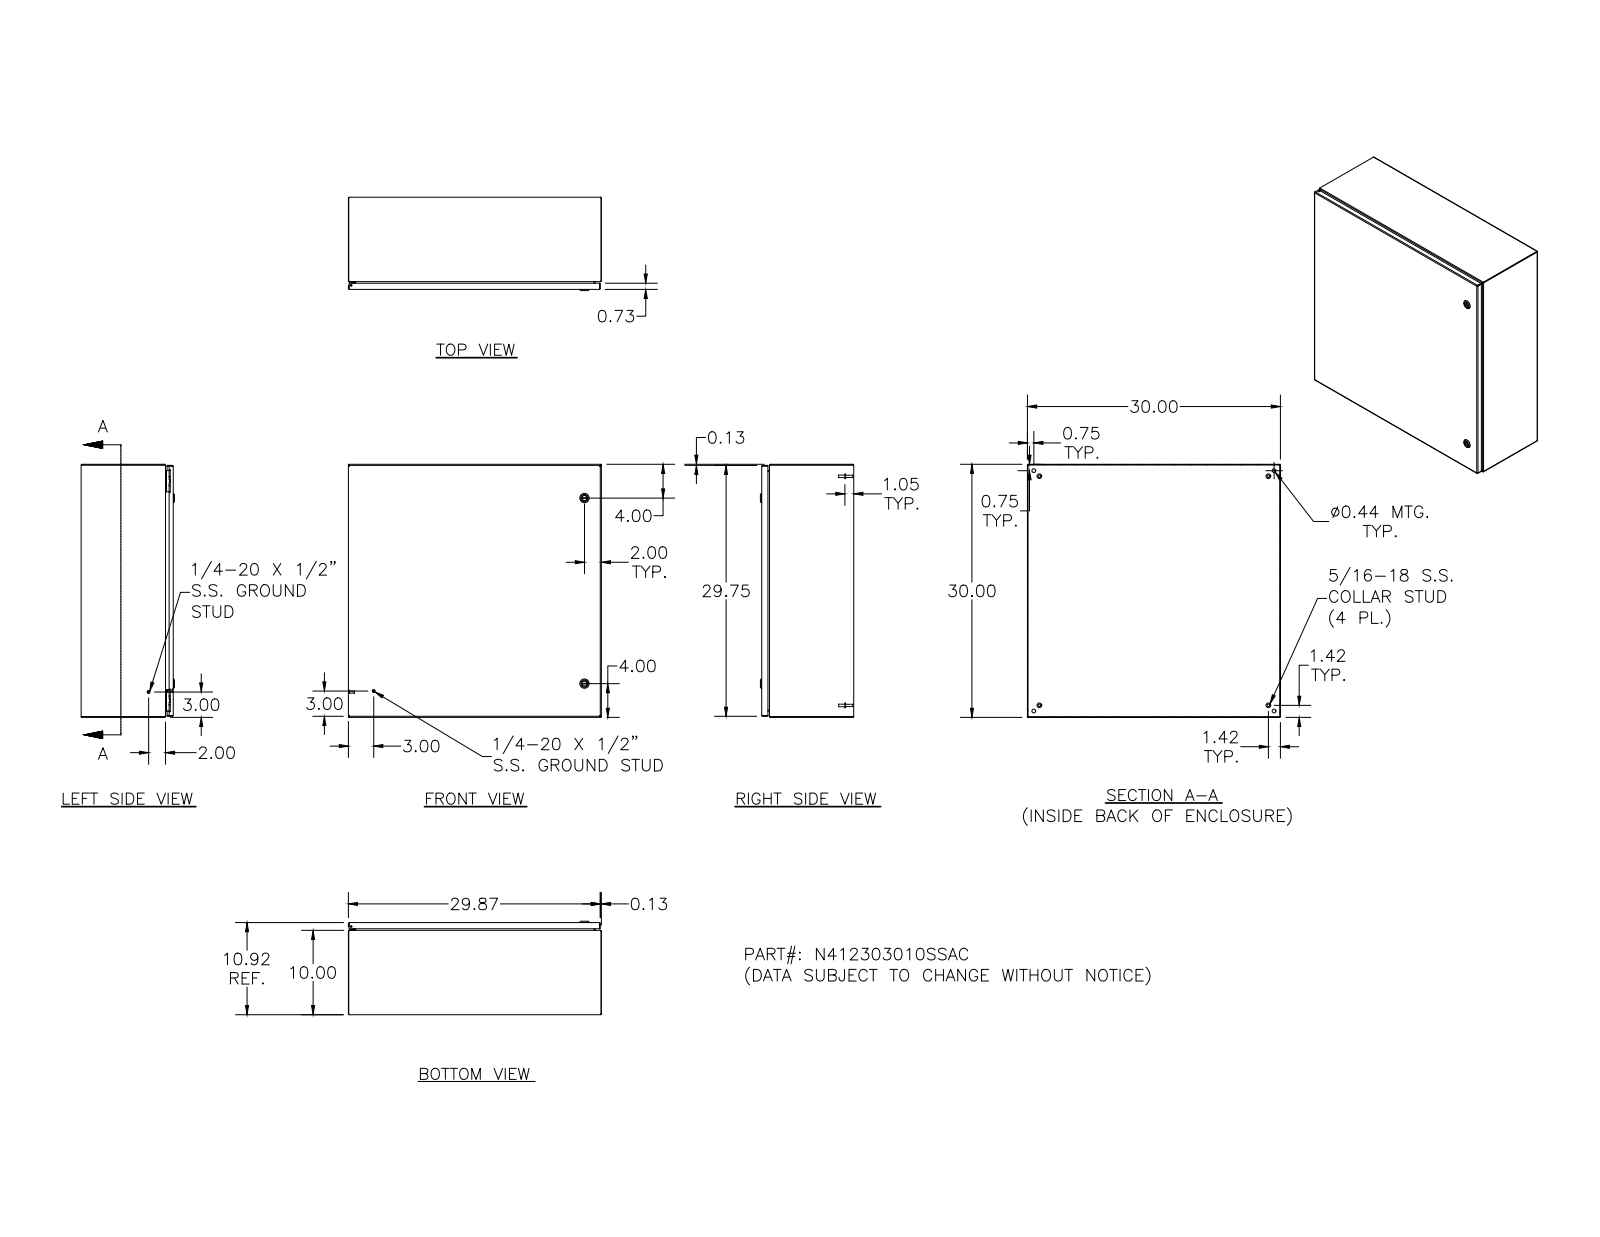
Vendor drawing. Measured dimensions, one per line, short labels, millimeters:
name: N412303010SSAC; N412303010SSACBKP; 388151; N4123030SSACLID (+8 more)
written by: Autodesk Inventor 2011 (AUTOMOTIVE_DESIGN)
unit: mm
bodies: 42 solids, 1662 faces (698 planar, 588 cylindrical, 376 other)
size: 762 × 762 × 281.3
volume: 3 935 000 mm³; area: 4 201 000 mm²
holes: 5× ⌀4.8, 4× ⌀2.4, 4× ⌀3.9, 4× ⌀4.2, 4× ⌀4.4, 4× ⌀11.1, 2× ⌀4, 2× ⌀5, 2× ⌀8, 2× ⌀10, 2× ⌀10.2, 2× ⌀16.1
bosses: 10× ⌀6.4, 4× ⌀14.3, 4× ⌀9.1, 4× ⌀8.1, 4× ⌀7.6, 4× ⌀7, 4× ⌀6.5, 4× ⌀4.2
rounds: 26× R1.3, 18× R0.4, 16× R0.4, 16× R2.3, 15× R0.5, 14× R0.8, 14× R3.2, 8× R0.8
face distances: 1.9, 275.4, 760.1, 277.3, 273.5, 758.2, 762, 252.1, 23.3, 18.8
hole spacings: 660.4, 0.4, 16.8, 723.9, 703.5, 0.5, 12.7, 16.5
